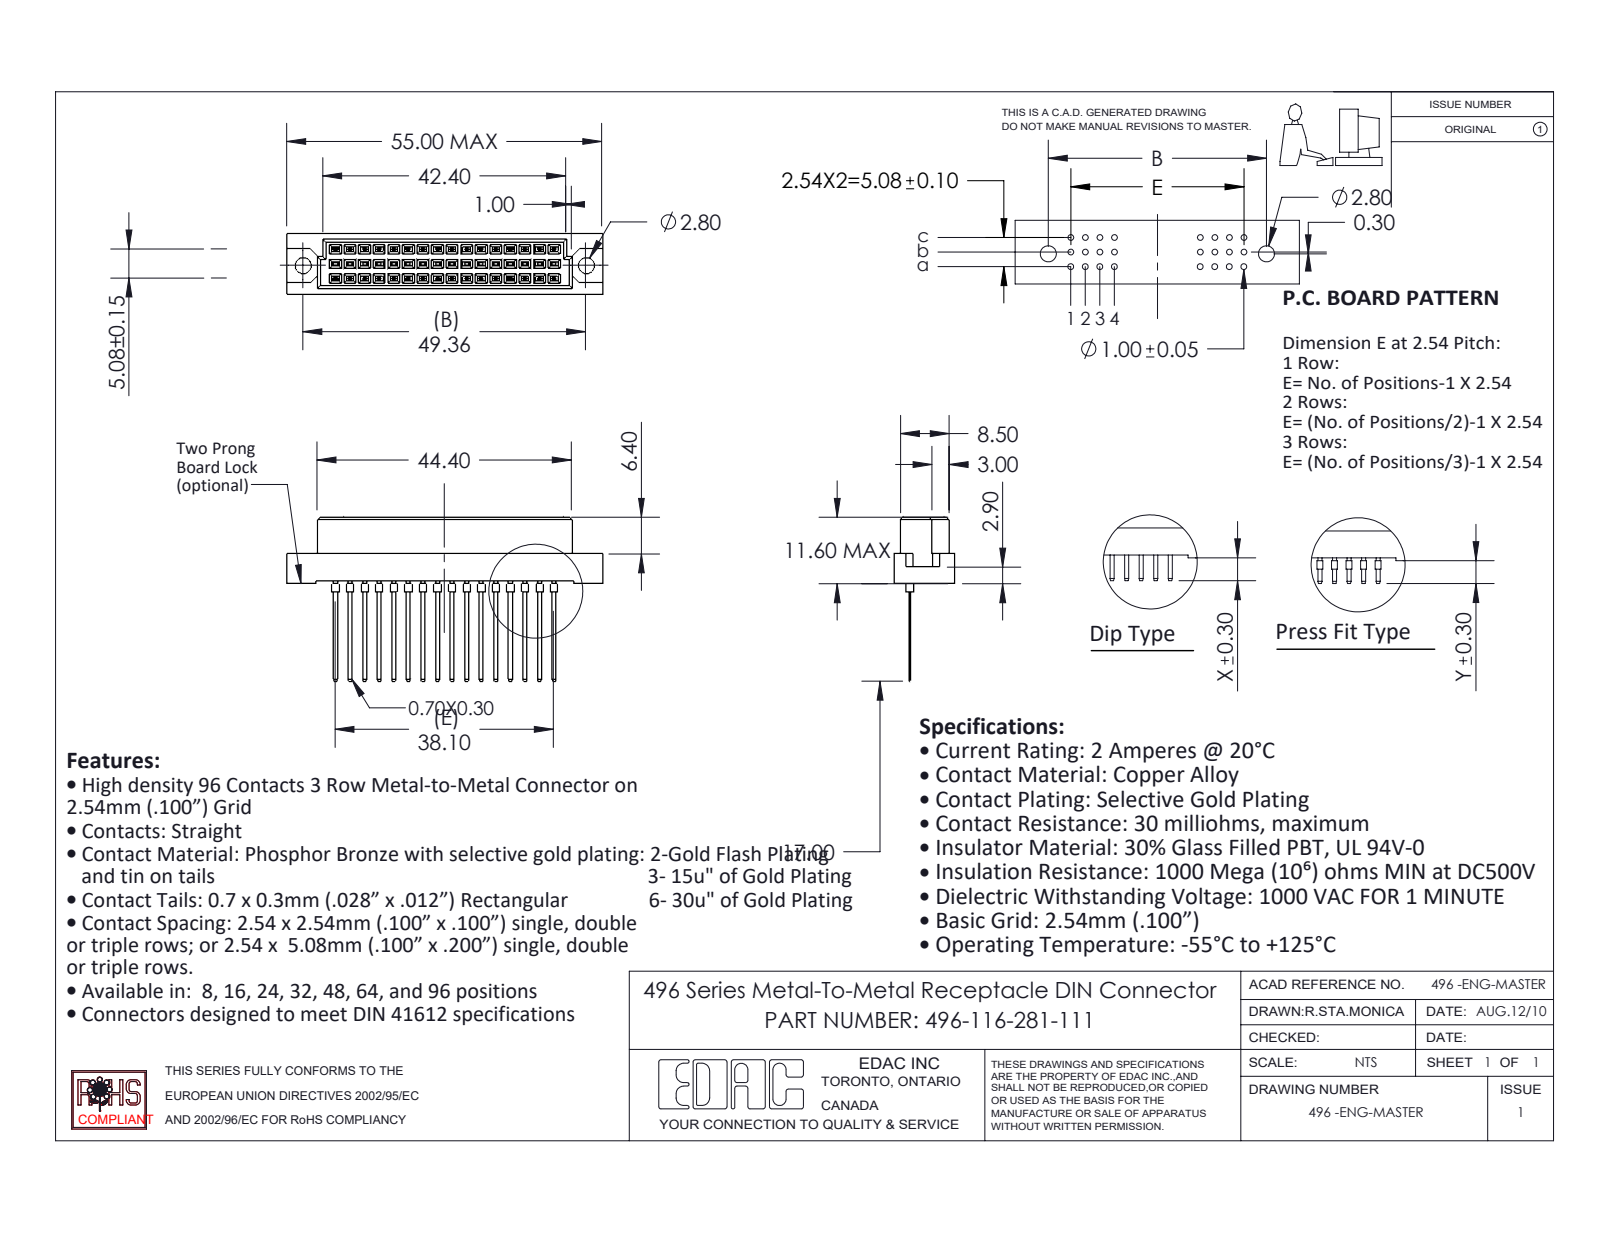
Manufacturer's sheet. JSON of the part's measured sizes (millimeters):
{"part_name": "496-116-281-111; 496-290_81; 496 Part_48", "step_written_by": "SolidWorks 2020 (CONFIG_CONTROL_DESIGN)", "units": "millimeters", "bodies": {"solids": 17, "faces": 954, "planar": 918, "cylindrical": 36, "other": 0}, "overall_size": [55, 28.6, 10.6], "volume_mm3": 4675, "surface_area_mm2": 4949, "round_holes": [[2.8, 2]], "round_bosses_or_shafts": [[1, 16]], "face_to_face_distances": [2.54, 5.08, 1.05, 9.55, 0.81, 2.91, 7.69, 2.61, 7.99, 1.86], "hole_center_spacings": [49.36]}
